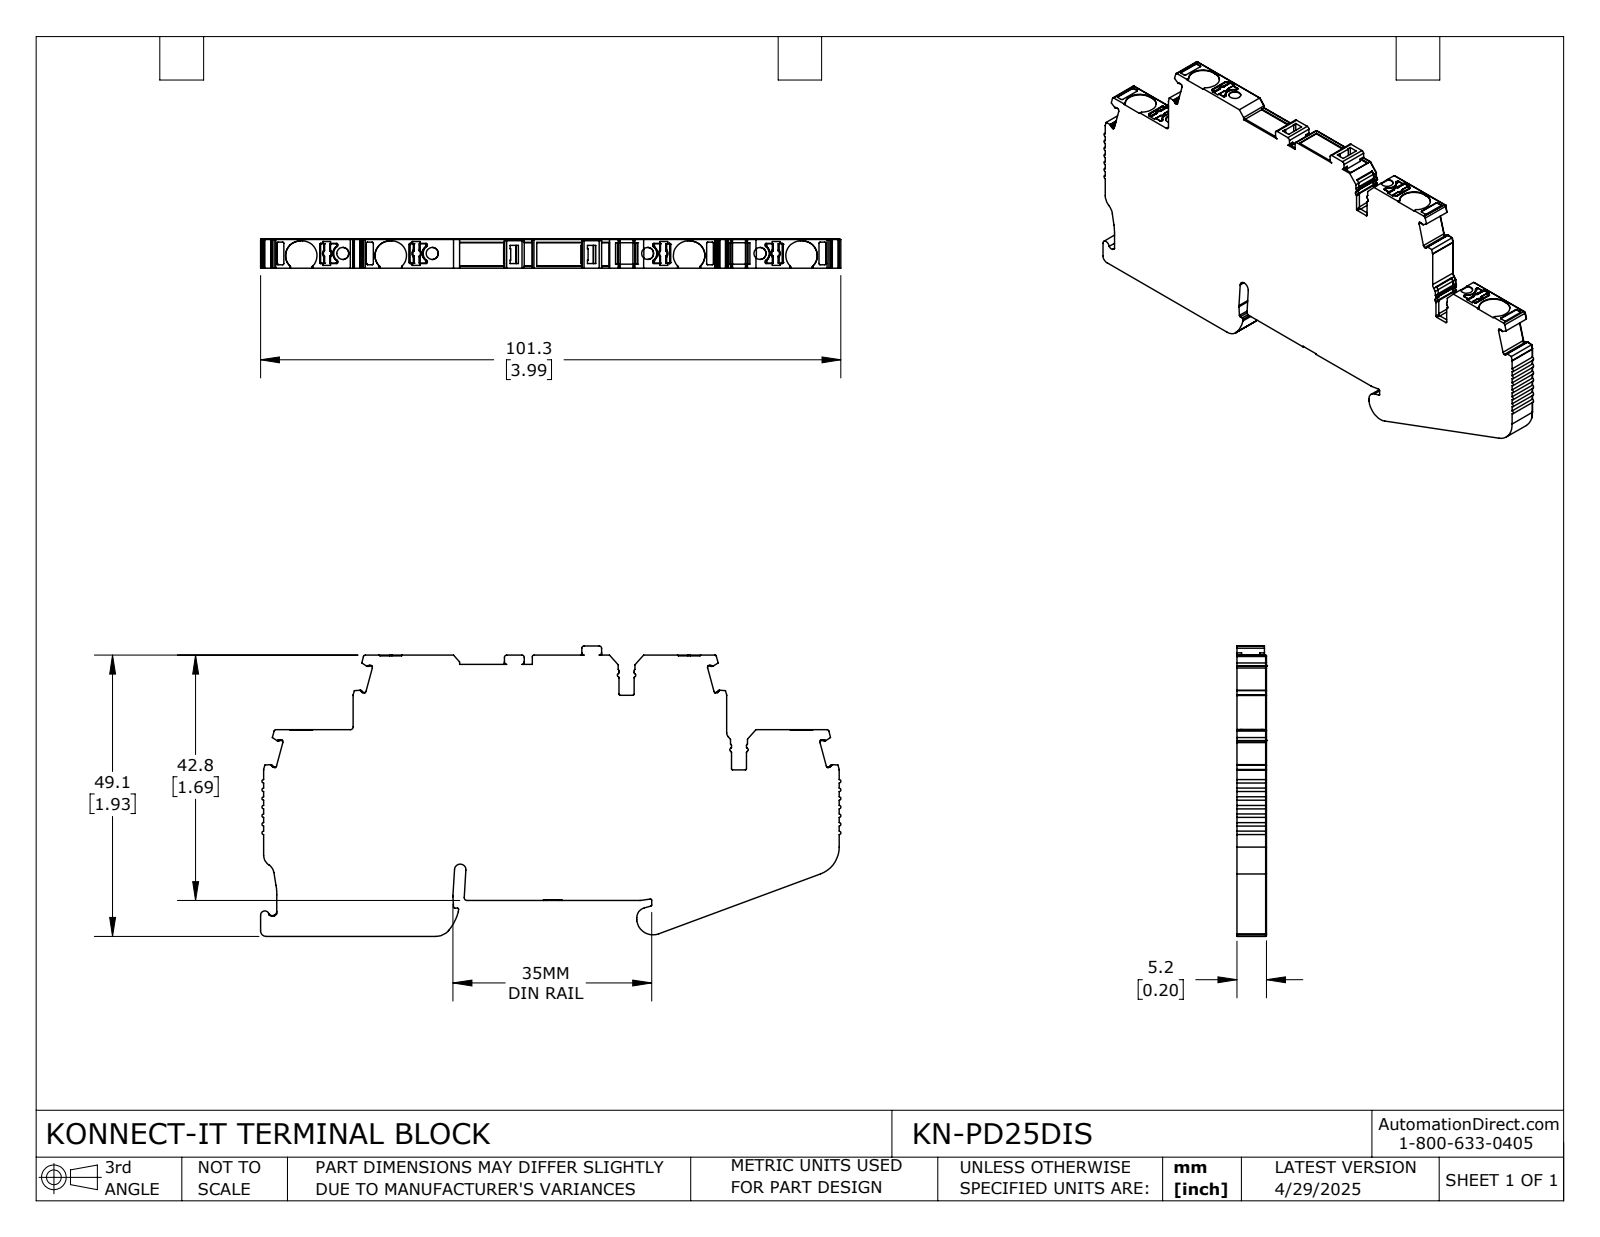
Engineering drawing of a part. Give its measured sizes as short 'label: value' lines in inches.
name: KN-PD25DIS
written by: SolidWorks 2024 (CONFIG_CONTROL_DESIGN)
unit: in
bodies: 1 solid, 883 faces (454 planar, 386 cylindrical, 43 other)
size: 3.99 × 1.996 × 0.203
volume: 1.229 in³; area: 15.22 in²
holes: 4× ⌀0.083
rounds: 85× R0.008, 38× R0.012, 25× R0.004, 16× R0.006, 13× R0.016, 13× R0.02, 9× R0.024, 8× R0.006
face distances: 0.203, 0.247, 0.512, 1.681, 1.928, 1.933, 1.686, 0.517, 1.169, 1.416
hole spacings: 0.615, 0.773, 1.481, 2.096, 2.254, 2.869
